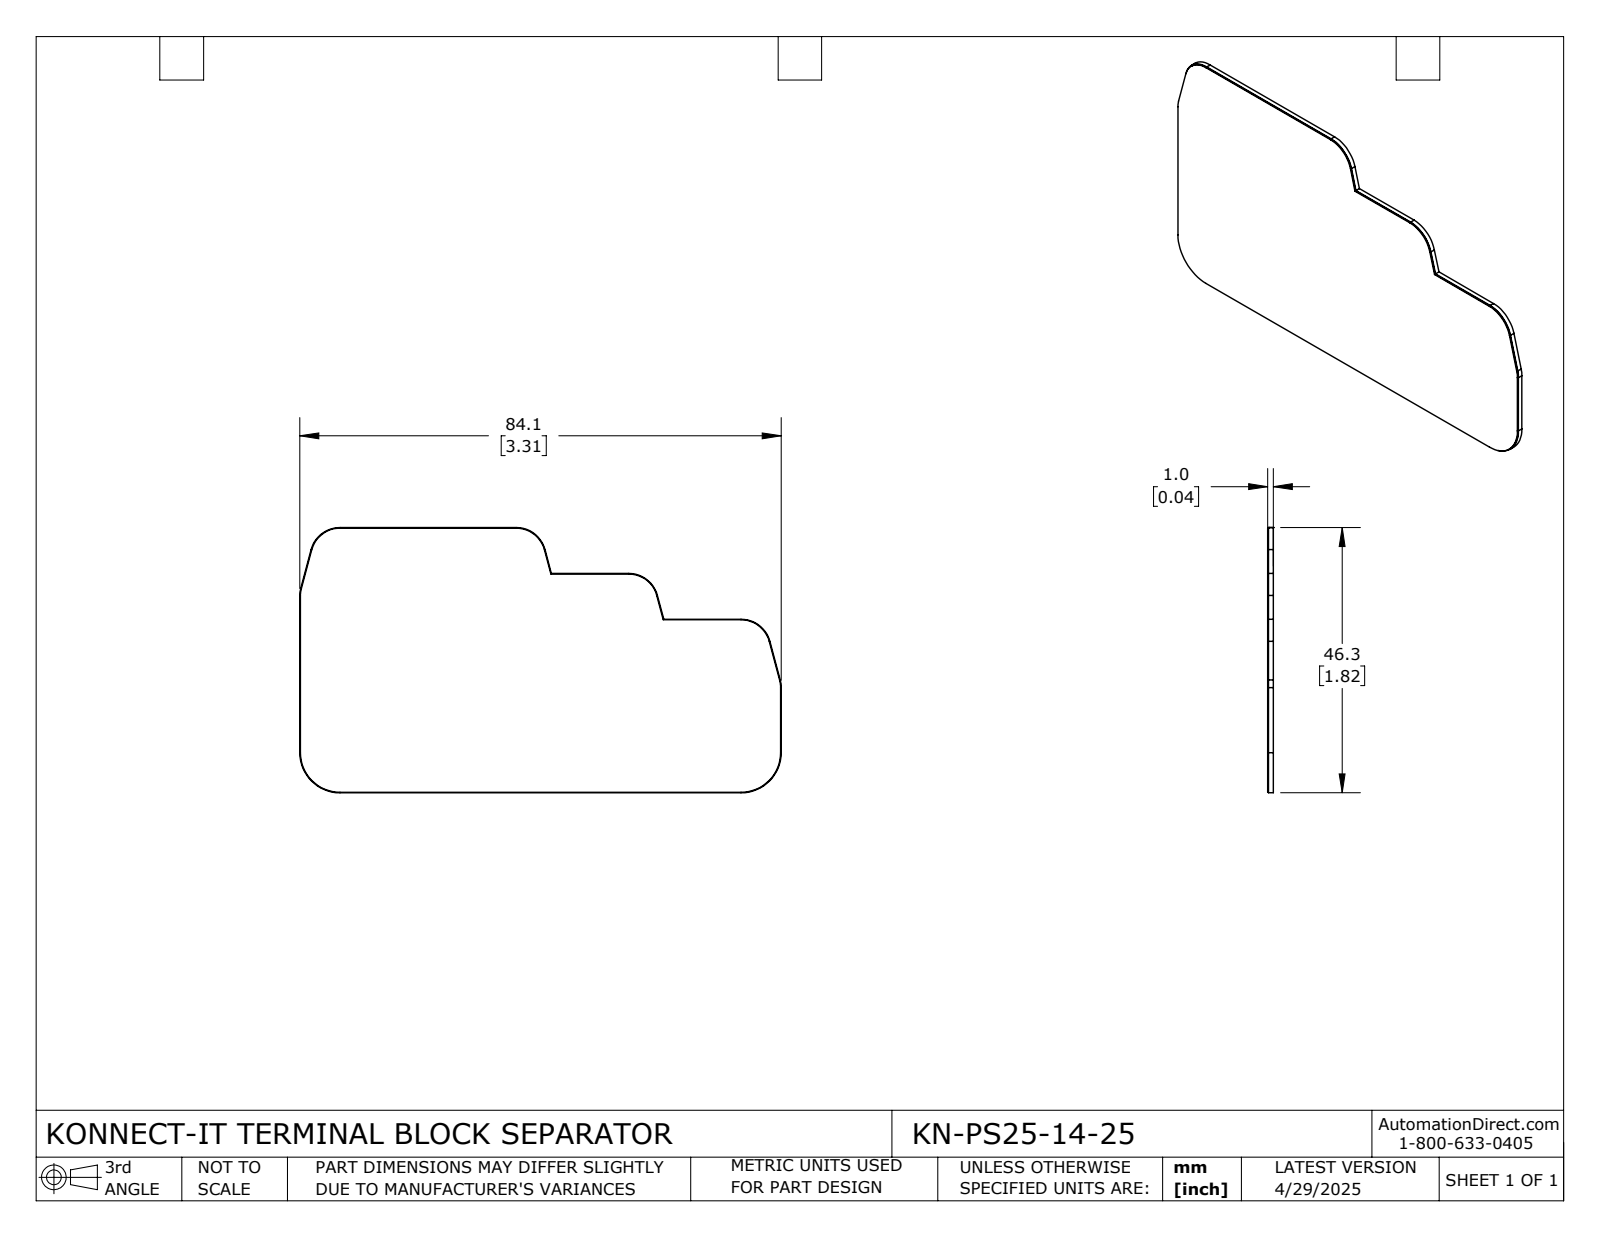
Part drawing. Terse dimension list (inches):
name: KN-PS25-14-25
written by: SolidWorks 2024 (CONFIG_CONTROL_DESIGN)
unit: in
bodies: 1 solid, 39 faces (23 planar, 16 cylindrical, 0 other)
size: 3.309 × 1.823 × 0.039
volume: 0.203 in³; area: 10.67 in²
rounds: 6× R0.201, 6× R0.205, 2× R0.272, 2× R0.276
face distances: 0.039, 0.315, 1.823, 0.033, 1.819, 0.63, 1.189, 1.504, 1.193, 1.508
